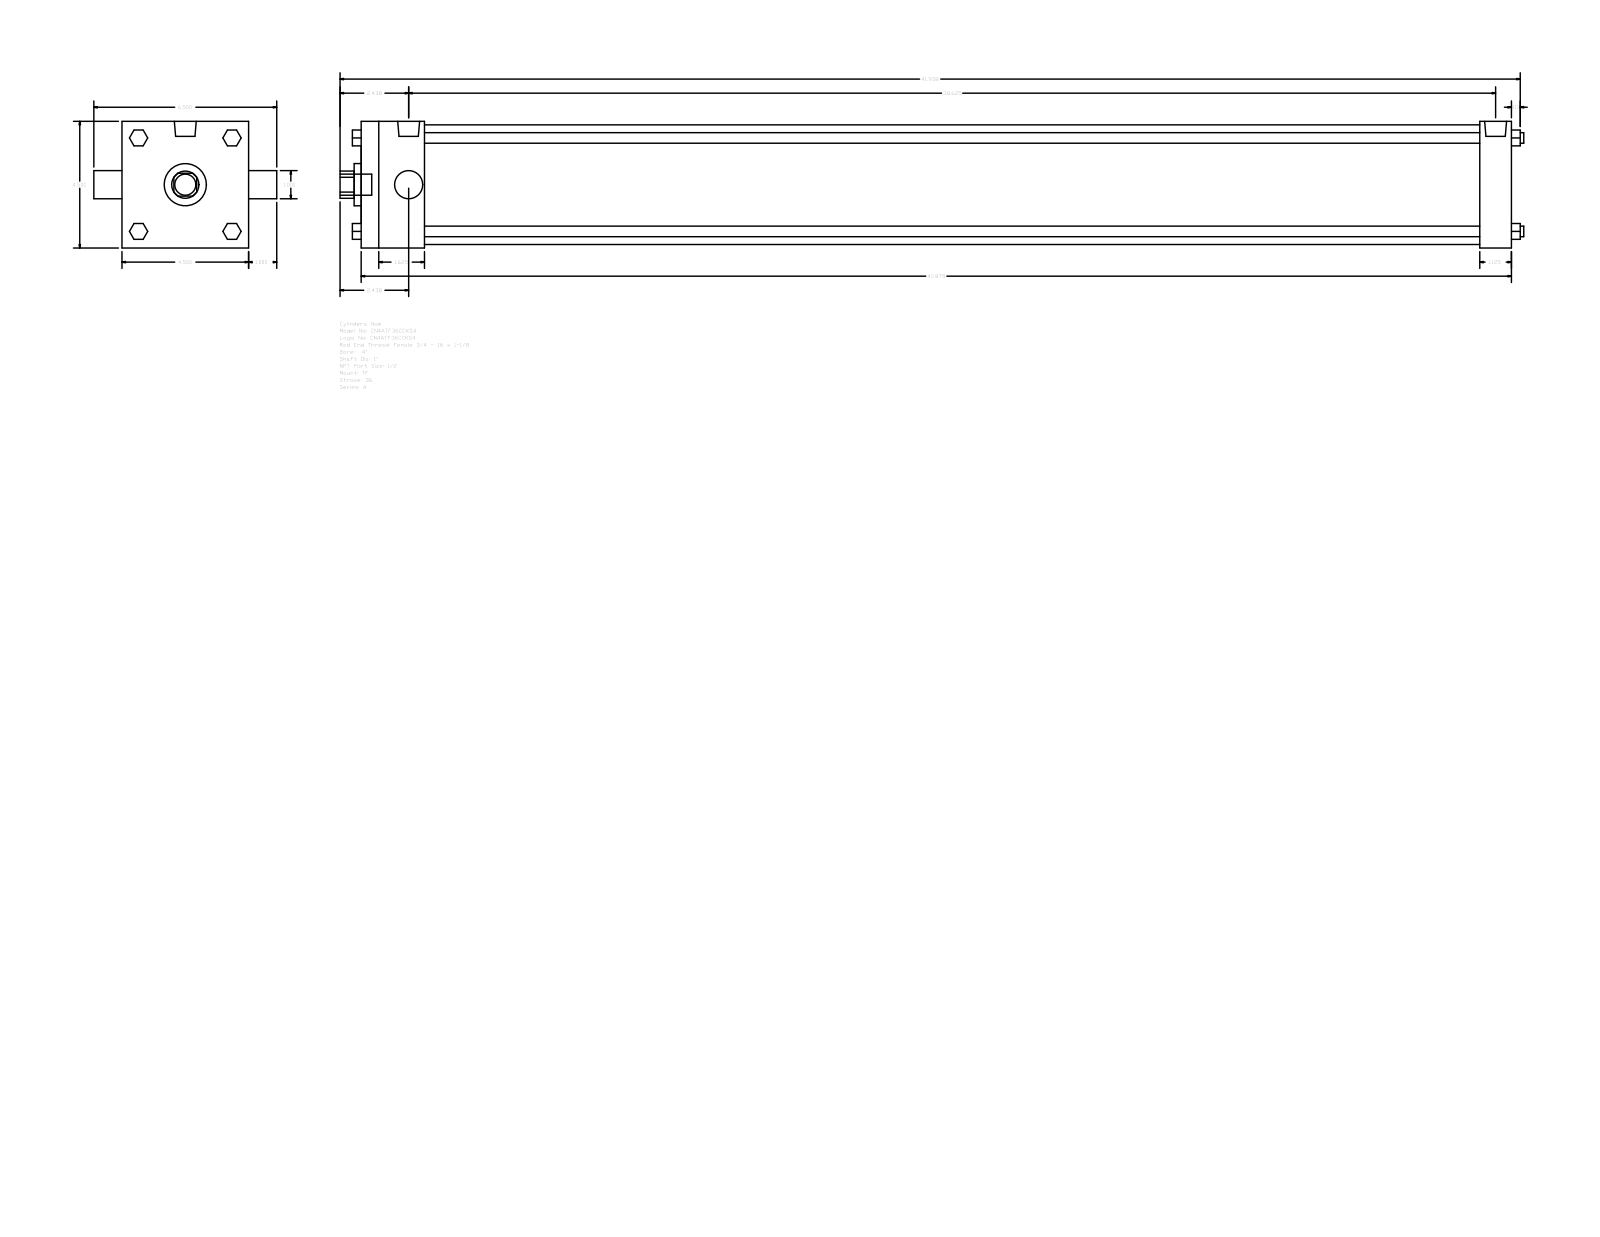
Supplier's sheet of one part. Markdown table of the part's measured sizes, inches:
| quantity | value |
| --- | --- |
| part name | A_TF__0400_1 |
| STEP written by | GSSL Pune (CONFIG_CONTROL_DESIGN) |
| units | inches |
| bodies | 0 solids, 120 faces (92 planar, 28 cylindrical, 0 other) |
| overall size | 42.063 × 6.5 × 4.5 |
| round holes (diameter × count) | 1 × 2, 1.5 × 1, 4.25 × 1 |
| round bosses / shafts (diameter × count) | 0.375 × 4, 0.344 × 3, 0.778 × 2, 0.75 × 1 |
| partial cylindrical surfaces (radius × count) | 0.484 × 1 |
| main face-to-face distances | 4.5, 40.875, 39.75, 1.125, 2.25, 37.5, 38.625, 0.563, 1.66, 2.875 |
